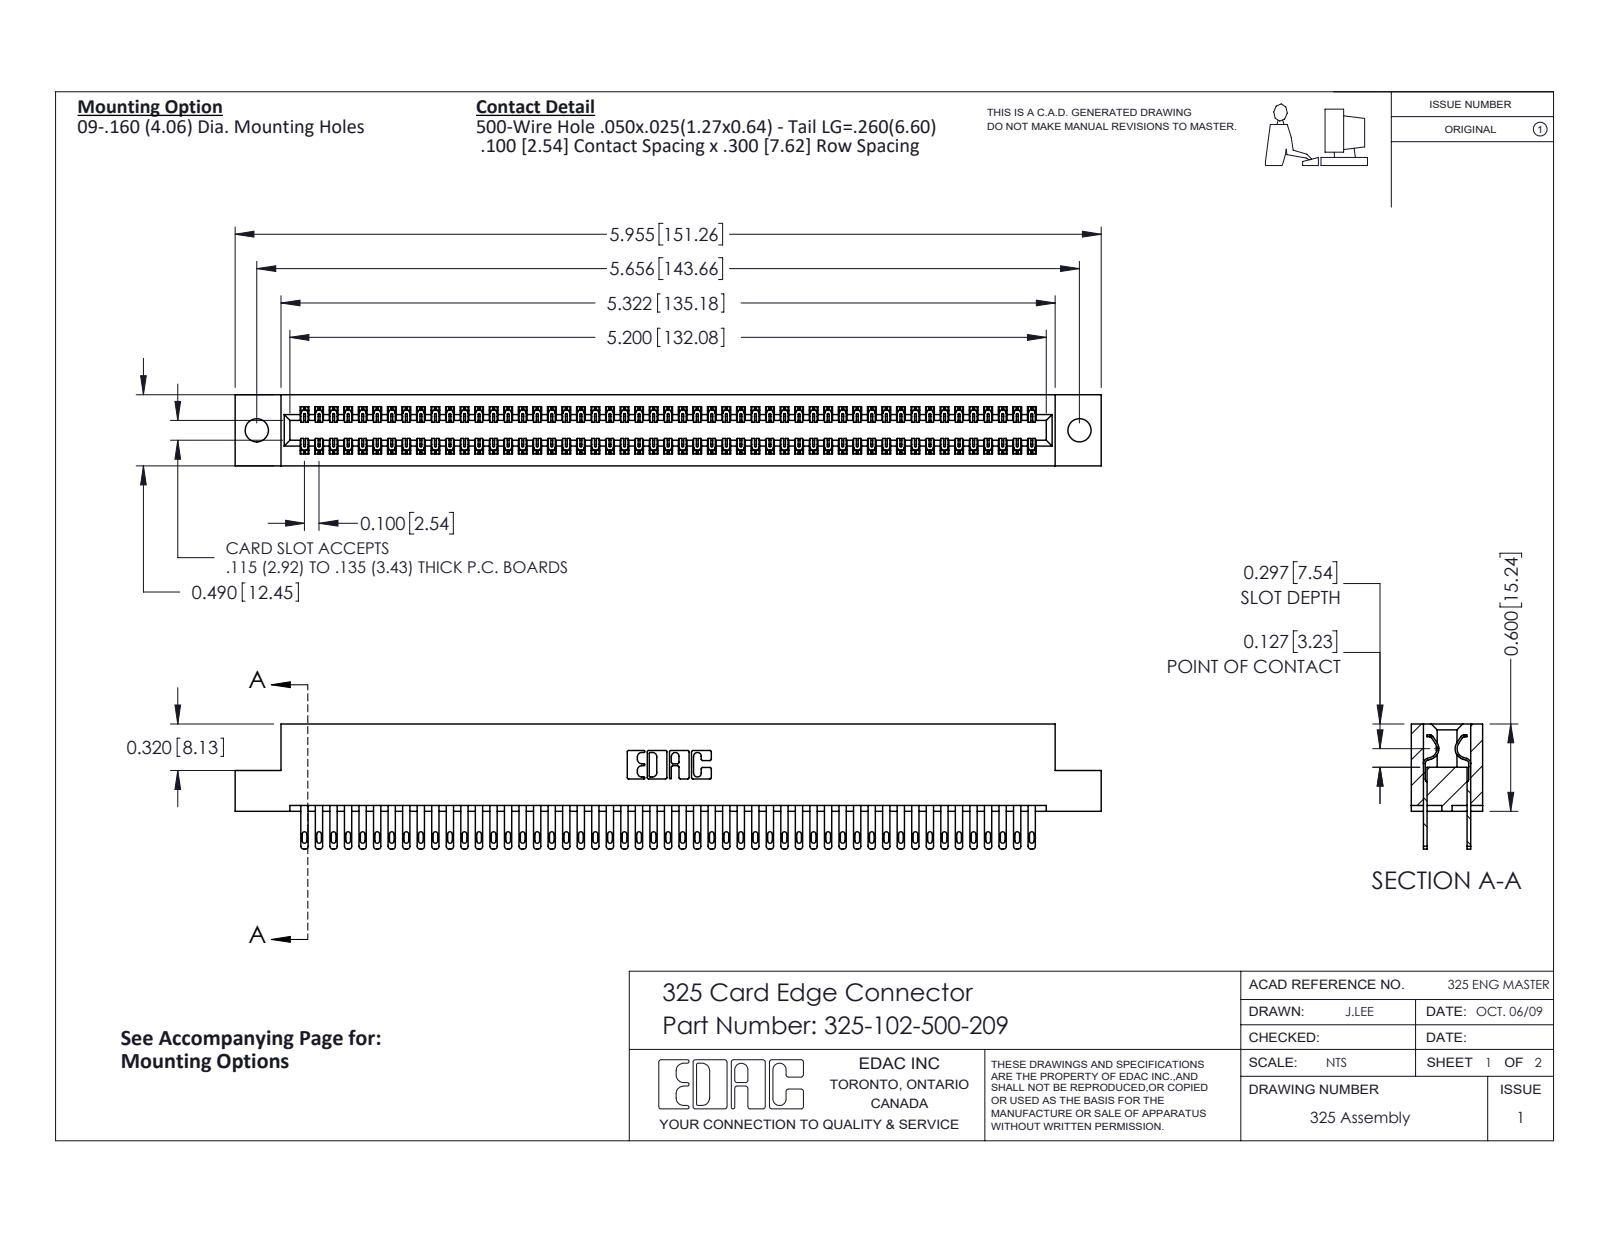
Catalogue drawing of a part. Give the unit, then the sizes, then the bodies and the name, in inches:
Units: inches
Overall size (bounding box): 5.955 × 0.86 × 0.49
Round holes (diameter × count): ⌀0.16 ×2
Partial cylindrical surfaces — rounded edges, fillets, slot ends (radius × count): R0.006 ×153, R0.016 ×102, R0.02 ×102, R0.01 ×22, R0.007 ×6, R0.031 ×6, R0.026 ×3, R0.014 ×2
Main face-to-face distances: 0.083, 0.407, 0.3, 0.107, 0.383, 0.025, 0.49, 0.325, 0.275, 0.56
Hole centre spacings: 5.656
Volume: 1.201 in³ · Surface area: 38.8 in²
Bodies: 103 solids, 5010 faces (3130 planar, 1880 cylindrical, 0 other)
Part name (STEP PRODUCT): 325 Part_.160 TH; 325-102-500-209; 325-292-001_325-293-100
STEP written by: SolidWorks 2016 (CONFIG_CONTROL_DESIGN)
